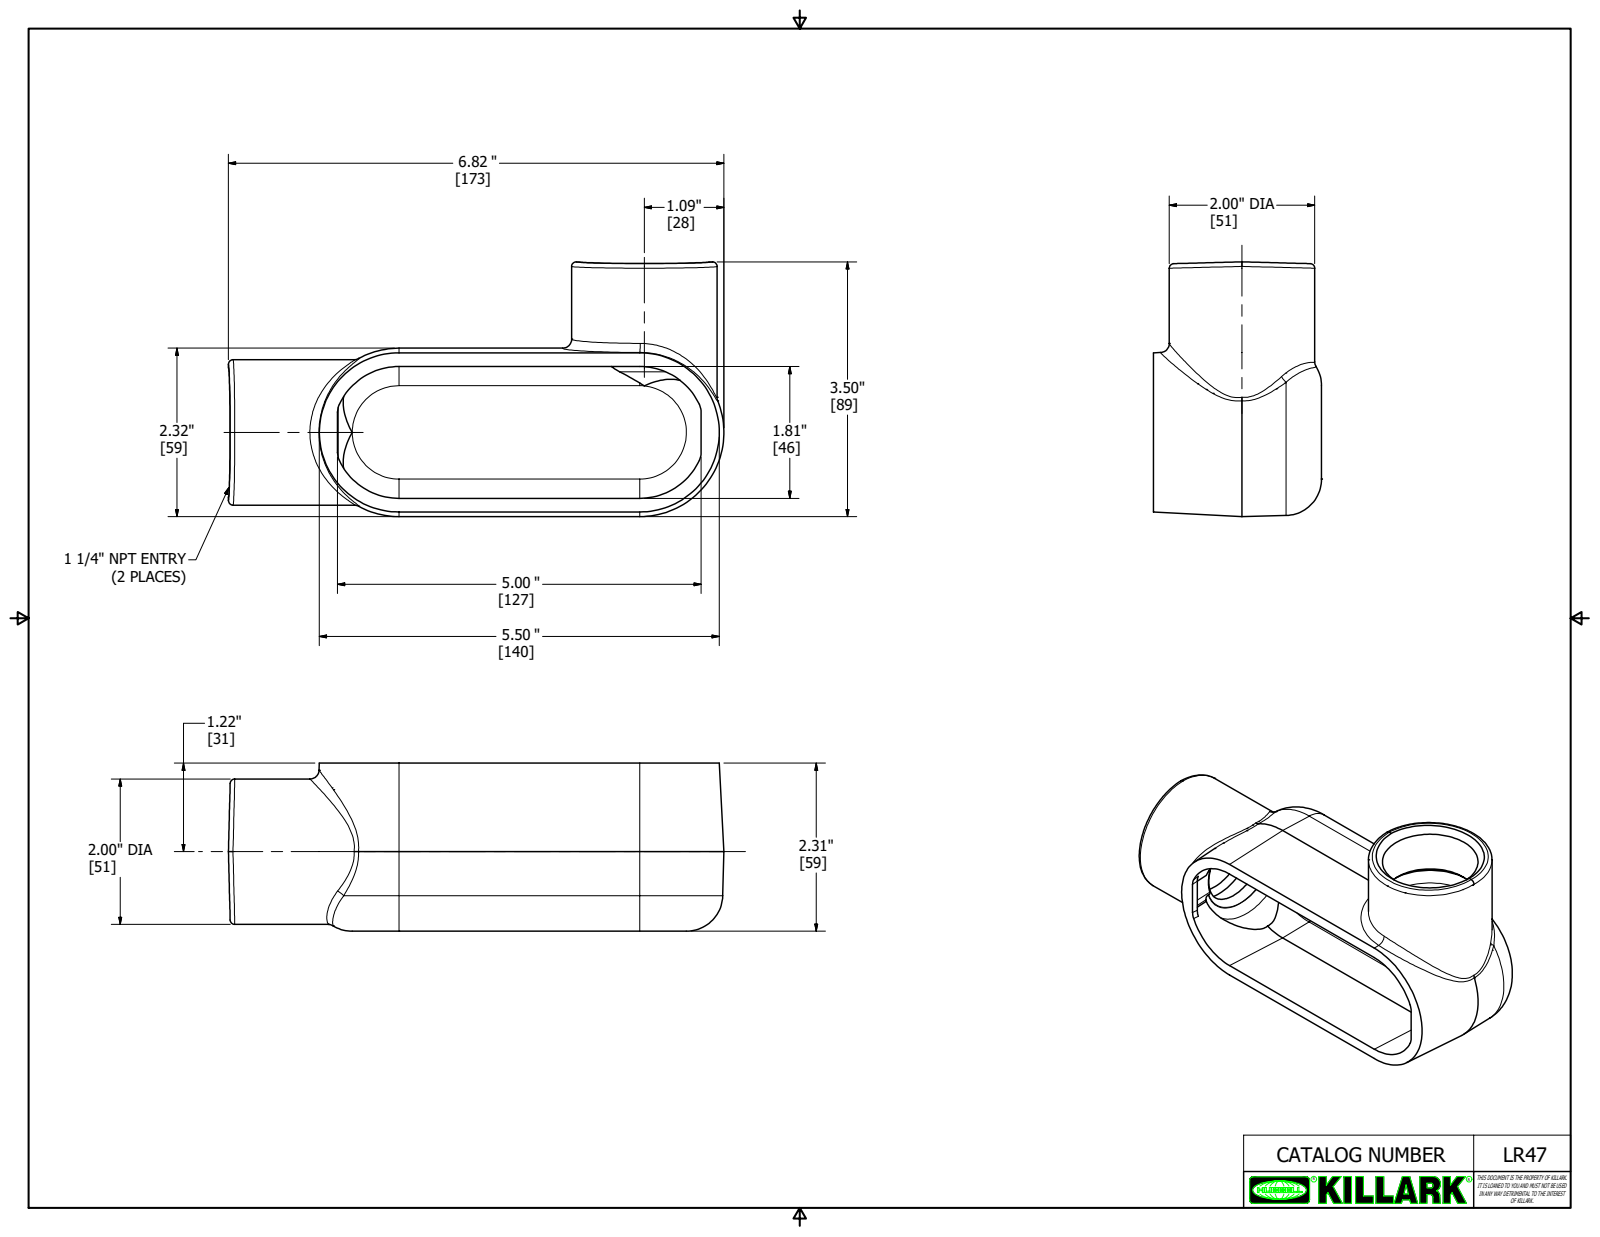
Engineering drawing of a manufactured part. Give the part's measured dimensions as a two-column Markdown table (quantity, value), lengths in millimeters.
| quantity | value |
| --- | --- |
| part name | 17684 |
| STEP written by | Autodesk Inventor 2018 (AUTOMOTIVE_DESIGN) |
| units | millimeters |
| bodies | 1 solid, 102 faces (36 planar, 18 cylindrical, 48 other) |
| overall size | 173.1 × 89 × 58.7 |
| volume | 153 600 mm³ |
| surface area | 66 320 mm² |
| round holes (diameter × count) | 42.3 × 2, 46.1 × 1 |
| round bosses / shafts (diameter × count) | 50.8 × 2 |
| partial cylindrical surfaces (radius × count) | 1.3 × 4, 3.2 × 4, 8 × 2, 12.7 × 2, 23 × 1 |
| main face-to-face distances | 4.7, 4.8, 58.7, 54, 0.8, 4, 57.9, 34.9, 30.1, 89 |
